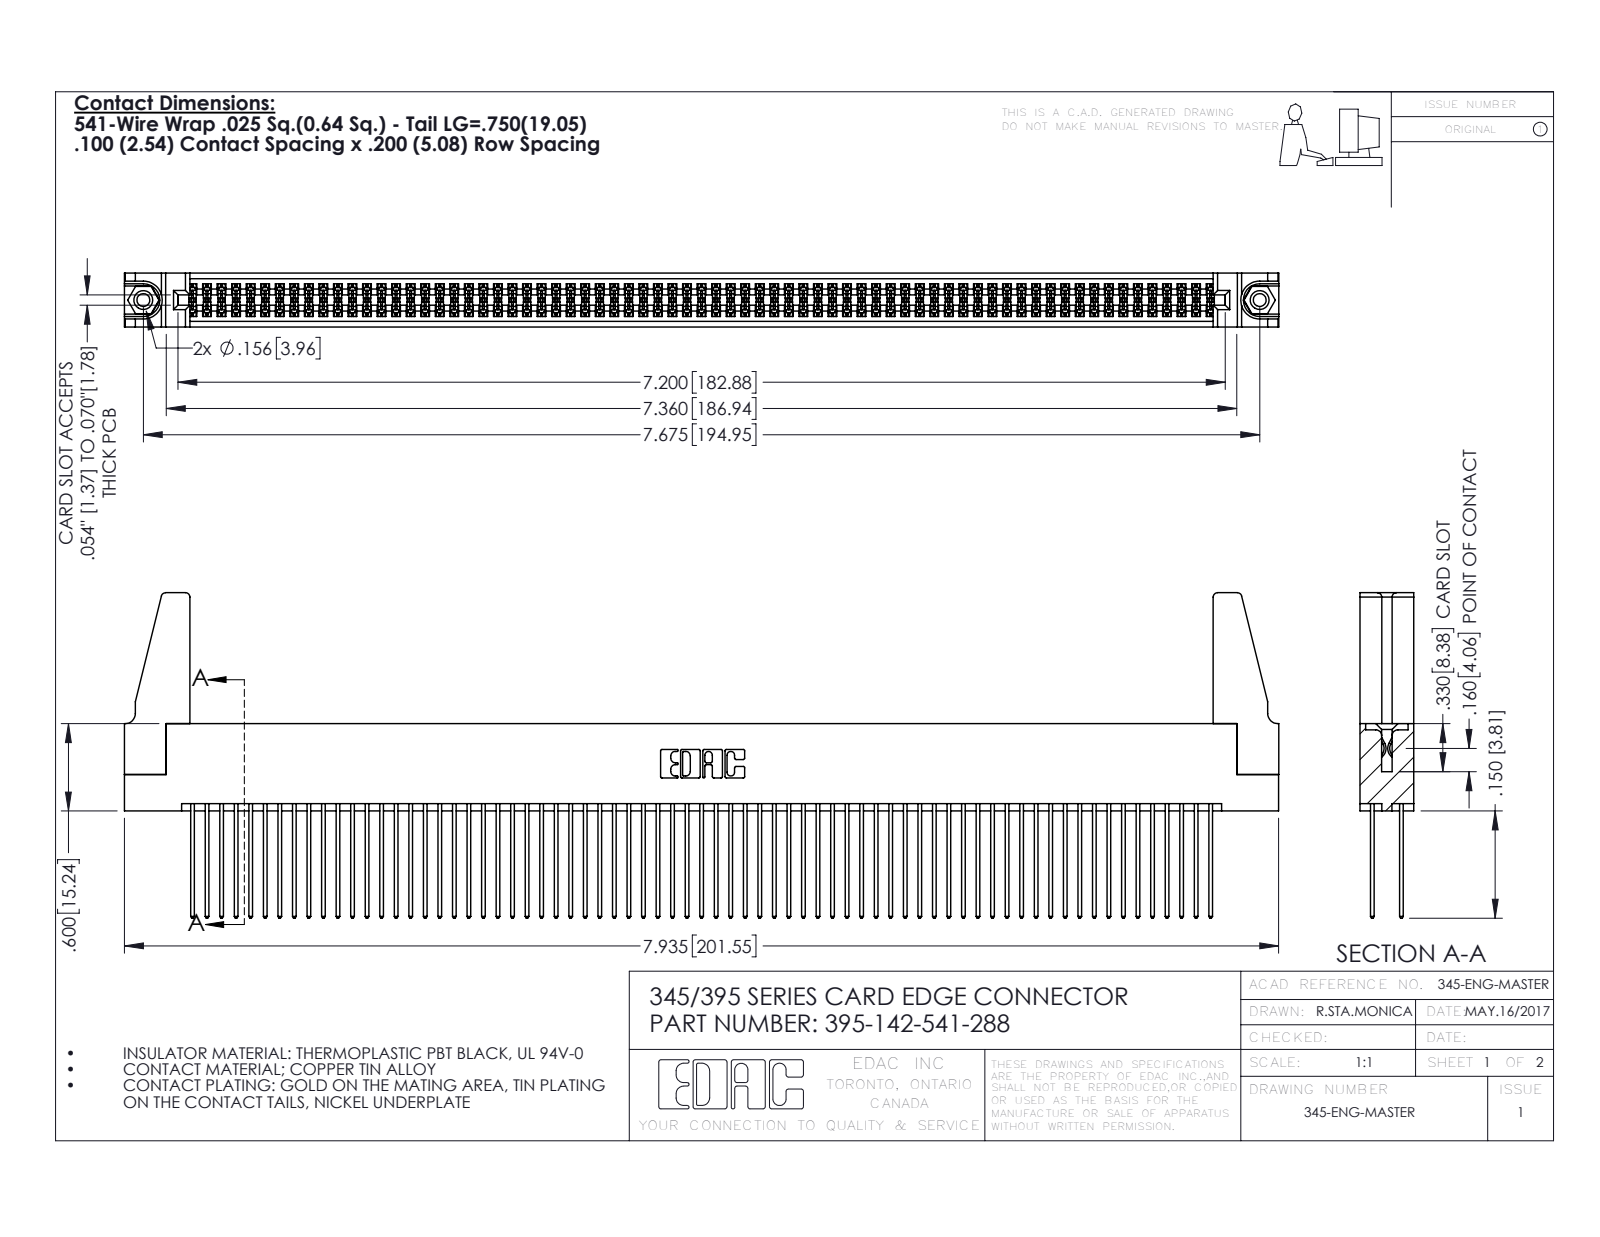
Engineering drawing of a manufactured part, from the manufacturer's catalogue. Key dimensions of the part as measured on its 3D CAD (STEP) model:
Part name (STEP PRODUCT): 345-292-001_345-293-141; 345-220-078_345-220-088; 395-142-541-288; 345-250-001_345-250-001-102 (+1 more)
STEP written by: SolidWorks 2016 (CONFIG_CONTROL_DESIGN)
Units: inches
Bodies: 147 solids, 7350 faces (4838 planar, 2496 cylindrical, 16 other)
Overall size (bounding box): 7.936 × 2.237 × 0.37
Volume: 1.46 in³ · Surface area: 58.99 in²
Round holes (diameter × count): ⌀0.089 ×2, ⌀0.125 ×2, ⌀0.156 ×2, ⌀0.064 ×1
Round bosses / shafts (diameter × count): ⌀0.155 ×2
Partial cylindrical surfaces — rounded edges, fillets, slot ends (radius × count): R0.006 ×213, R0.01 ×142, R0.01 ×22, R0.03 ×8, R0.007 ×6, R0.031 ×6, R0.026 ×3, R0.014 ×2
Main face-to-face distances: 0.072, 0.298, 0.2, 0.098, 0.272, 0.025, 0.37, 0.225, 0.175, 0.149
Hole centre spacings: 0.27, 7.439, 7.675
